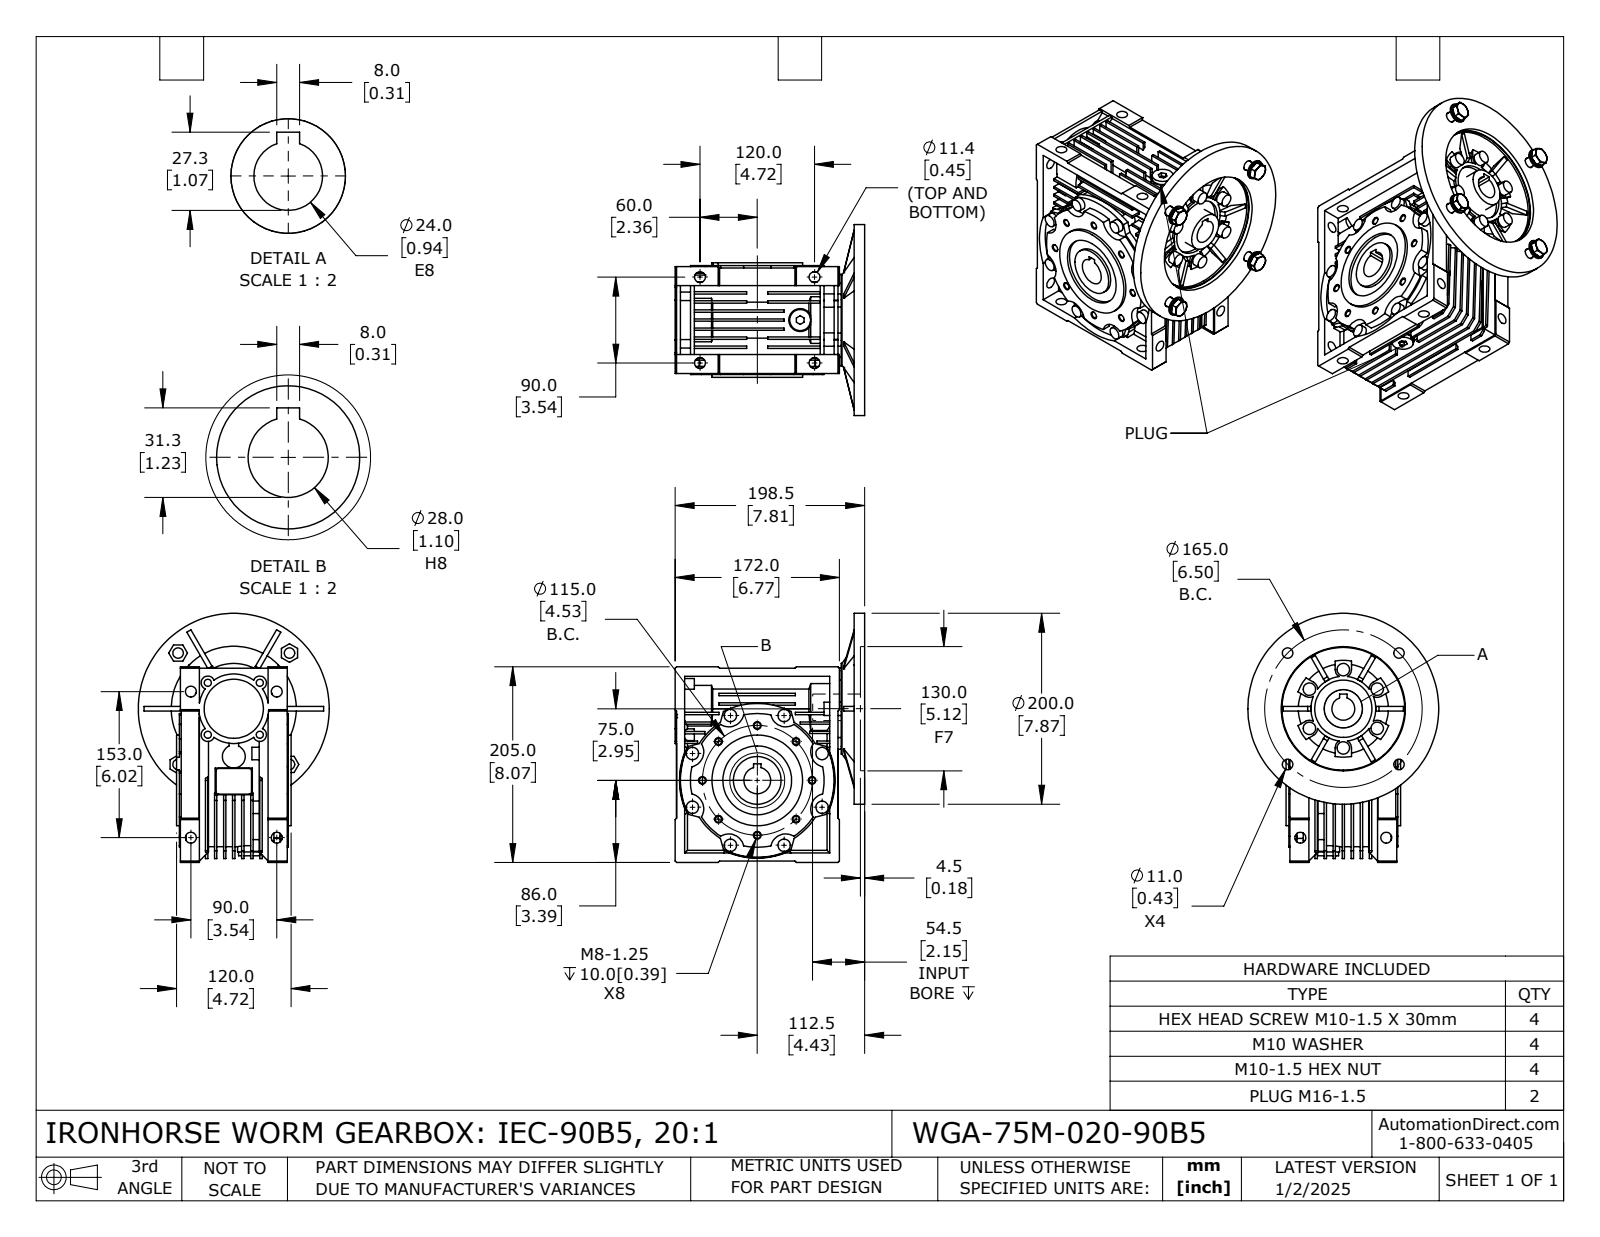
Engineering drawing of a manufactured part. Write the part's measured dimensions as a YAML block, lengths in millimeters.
part_name: "WGA-75M-020-90B5"
step_written_by: "SolidWorks 2024 (CONFIG_CONTROL_DESIGN)"
units: millimeters
bodies: {solids: 20, faces: 1475, planar: 818, cylindrical: 439, other: 218}
overall_size: [261, 216.93, 200]
volume: 3036000
surface_area: 538373
round_holes:
  - {diameter: 6.65, count: 8}
  - {diameter: 11.38, count: 8}
  - {diameter: 7.45, count: 4}
  - {diameter: 8.5, count: 4}
  - {diameter: 10, count: 4}
  - {diameter: 10.5, count: 4}
  - {diameter: 11, count: 4}
  - {diameter: 14.5, count: 2}
  - {diameter: 24, count: 1}
  - {diameter: 25, count: 1}
  - {diameter: 28, count: 1}
  - {diameter: 39, count: 1}
round_bosses_or_shafts:
  - {diameter: 13, count: 14}
  - {diameter: 20, count: 4}
  - {diameter: 16, count: 4}
  - {diameter: 24, count: 3}
  - {diameter: 95, count: 2}
  - {diameter: 22, count: 2}
  - {diameter: 15.8, count: 2}
  - {diameter: 13.7, count: 2}
partial_cylinders:
  - {radius: 7, count: 10}
  - {radius: 16, count: 8}
  - {radius: 8.5, count: 6}
  - {radius: 2.5, count: 4}
  - {radius: 33.99, count: 1}
  - {radius: 36, count: 1}
  - {radius: 36.5, count: 1}
  - {radius: 39, count: 1}
face_to_face_distances: [9.5, 2.5, 19, 12, 7, 28.5, 10, 16.5, 27.75, 21.5]
hole_center_spacings: [44.01, 57.5, 81.32, 91.04, 106.25, 38.49, 54.44, 82.51]
